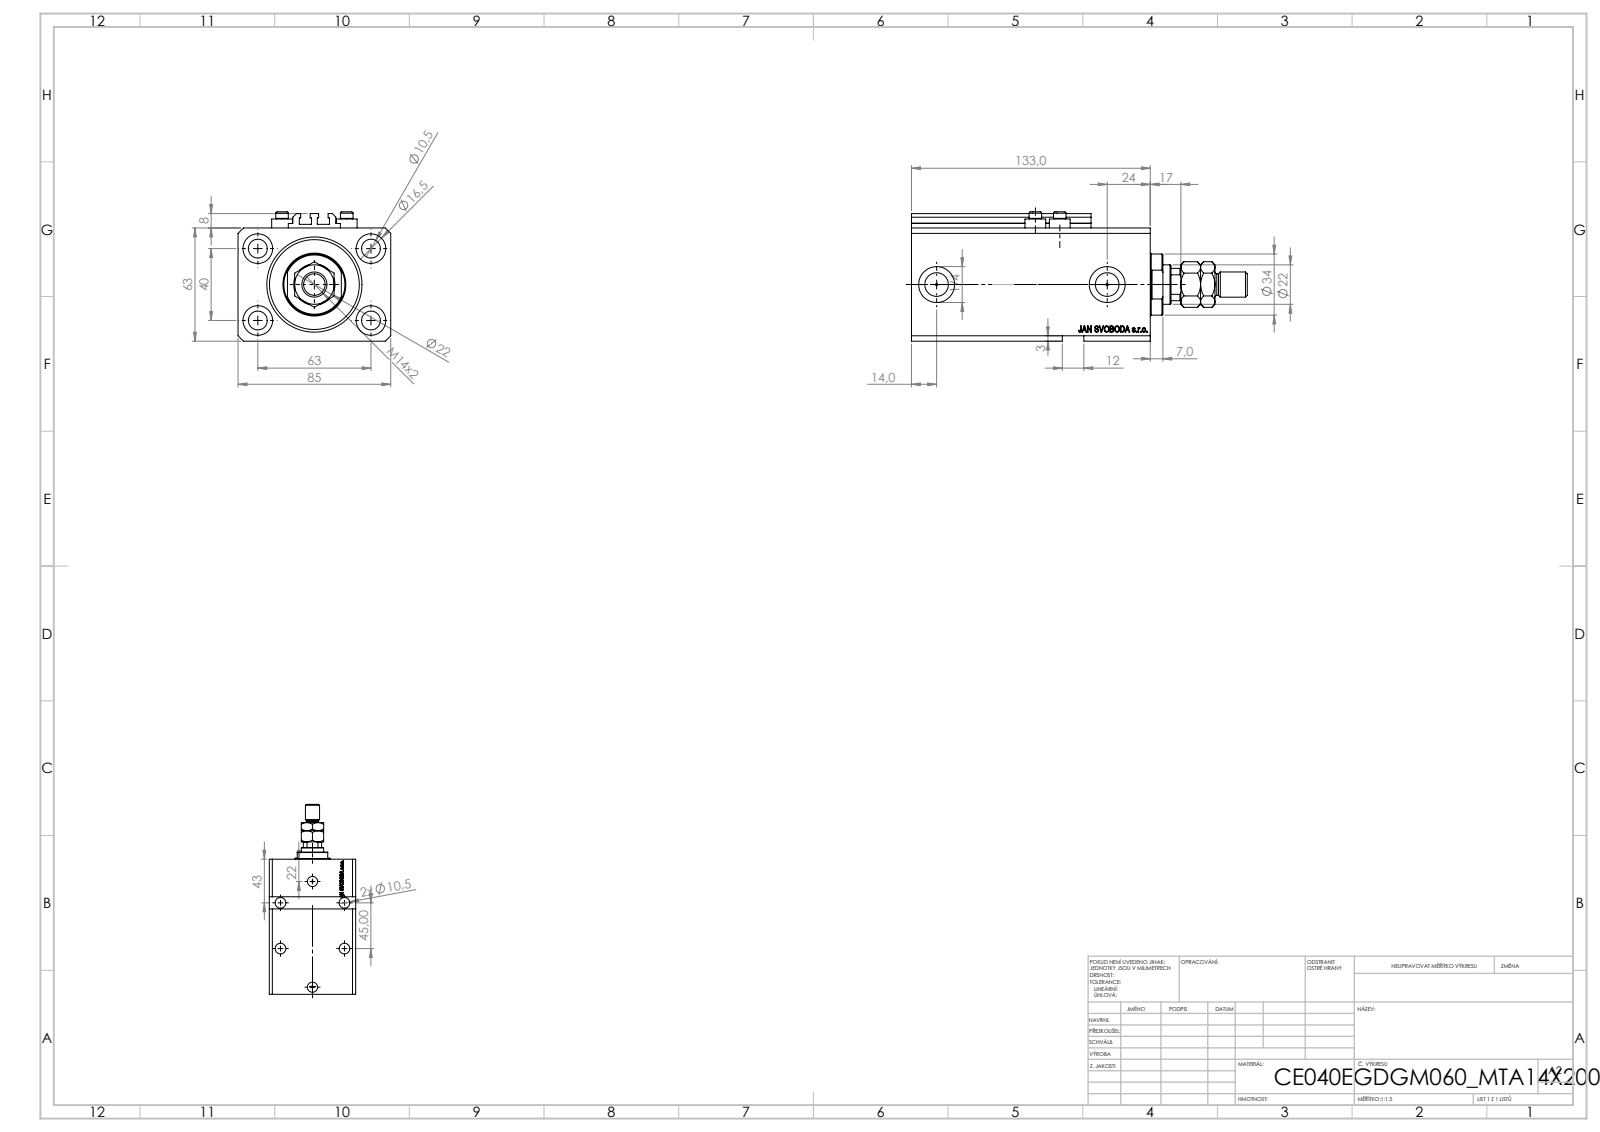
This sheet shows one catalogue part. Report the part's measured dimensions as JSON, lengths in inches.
{"part_name": "ALLEN BOLT V250CE; V250CE_C_VCP; V250CE_E_Body; V250CE_VC_E (+1 more)", "step_written_by": "SolidWorks 2019 (CONFIG_CONTROL_DESIGN)", "units": "inches", "bodies": {"solids": 9, "faces": 1172, "planar": 554, "cylindrical": 162, "other": 456}, "overall_size": [7.362, 3.346, 2.835], "volume_in3": 36.98, "surface_area_in2": 202.6, "round_holes": [[0.413, 8], [0.049, 4], [0.157, 4], [0.65, 4], [0.394, 2], [0.518, 2], [0.787, 2], [0.492, 1], [0.866, 1], [1.575, 1], [2.087, 1]], "round_bosses_or_shafts": [[0.457, 4], [0.276, 4], [1.339, 1], [0.551, 1], [0.472, 1]], "partial_cylinders_radius": [[0.008, 10], [0.413, 1]], "face_to_face_distances": [2.48, 3.346, 0.669, 5.236, 4.567, 0.449, 4.118, 4.787, 2.559, 0.118], "hole_center_spacings": [1.469, 2.48, 0.535, 0.606, 0.983, 1.084, 1.324, 1.417]}
